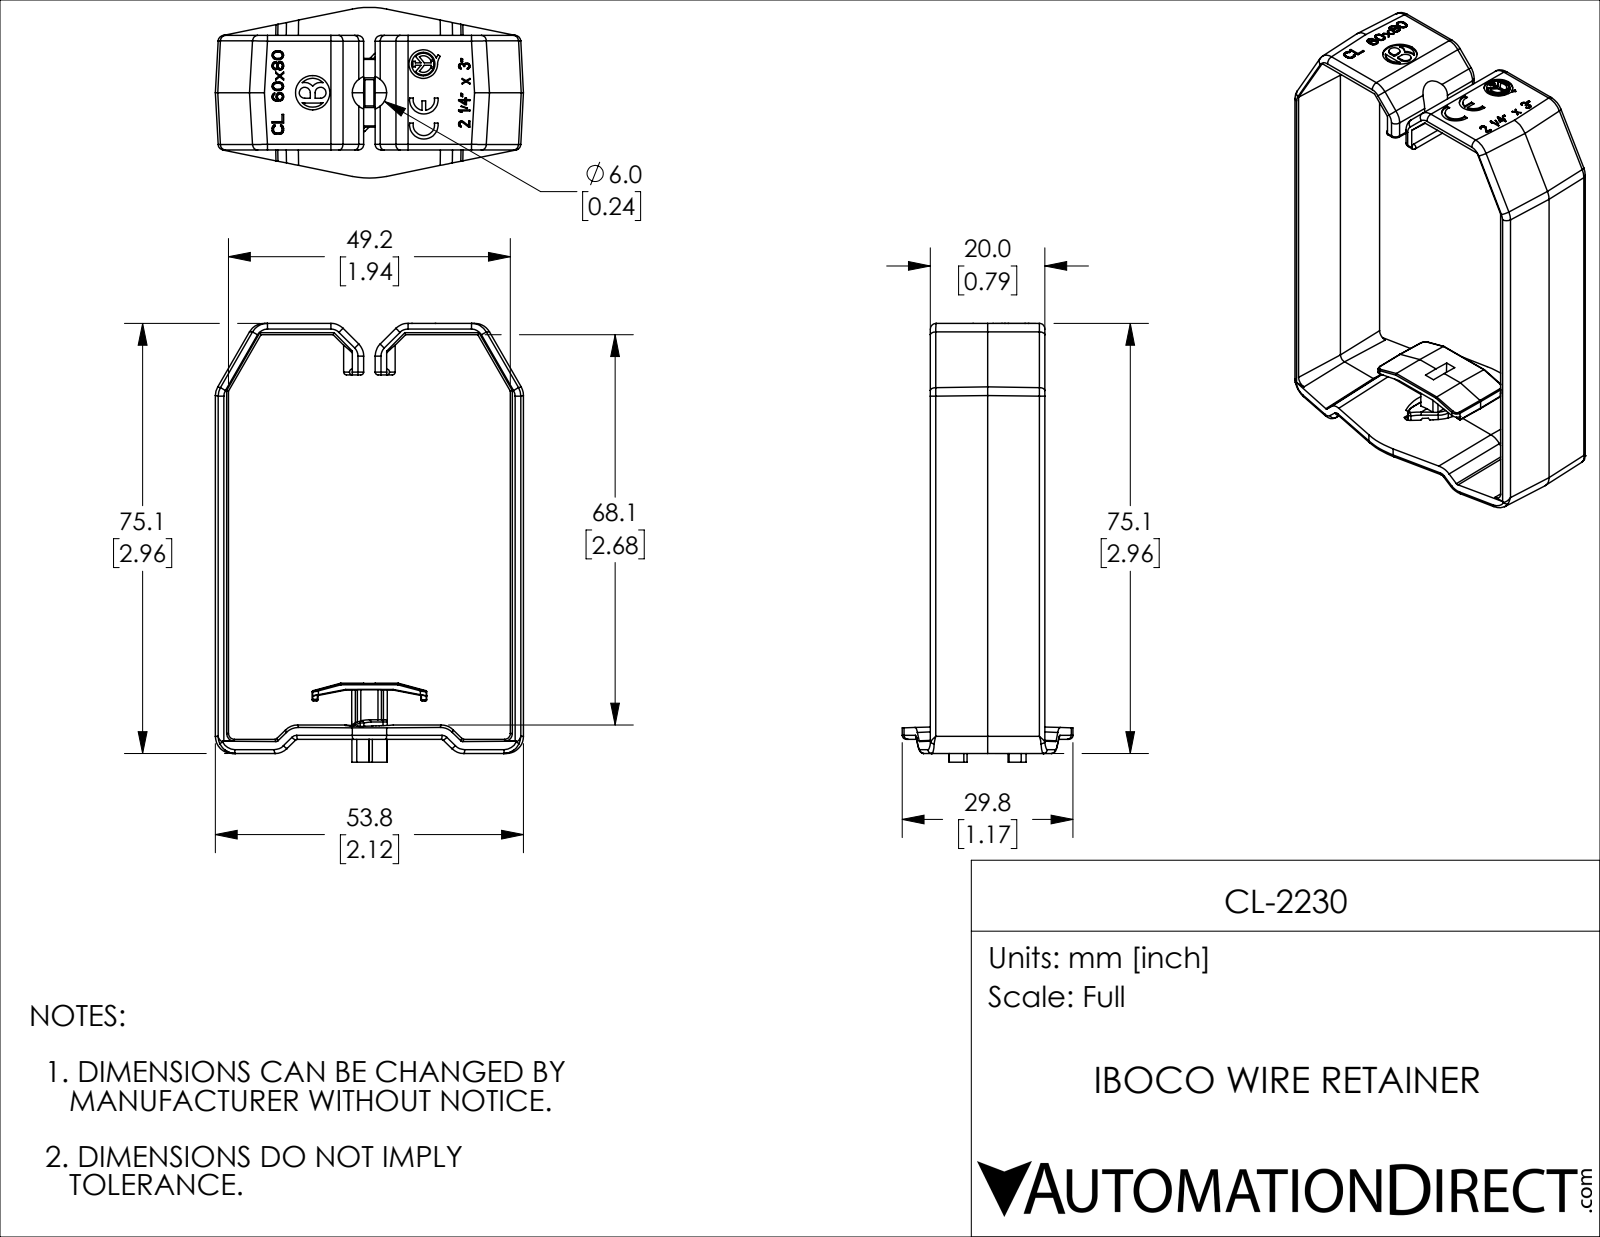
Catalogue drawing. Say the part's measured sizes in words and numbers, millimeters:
The part is named "CL-2230". Its 3-D file was written by "SolidWorks 2019 (CONFIG_CONTROL_DESIGN)". It is 1 solid with 862 faces: 620 planar, 180 cylindrical and 62 other. Overall it measures 76.6 by 53.8 by 29.8 millimeters. Its volume is 10 300 cubic millimeters and its surface area 12 070 square millimeters. Round holes: 1 of diameter 5, 1 of diameter 6. Round bosses or shafts: 1 of diameter 4.1. Partial cylindrical surfaces (rounded edges, fillets, slot ends): 24 of radius 1, 23 of radius 3, 22 of radius 0.2, 18 of radius 0.5, 12 of radius 0.7, 6 of radius 0.3, 6 of radius 0.4, 4 of radius 2.5. The main face-to-face distances are 49.1, 53.7, 2.5, 68, 72.6, 70.5, 75.1, 2, 4, 20. The hole center spacings are 20.
